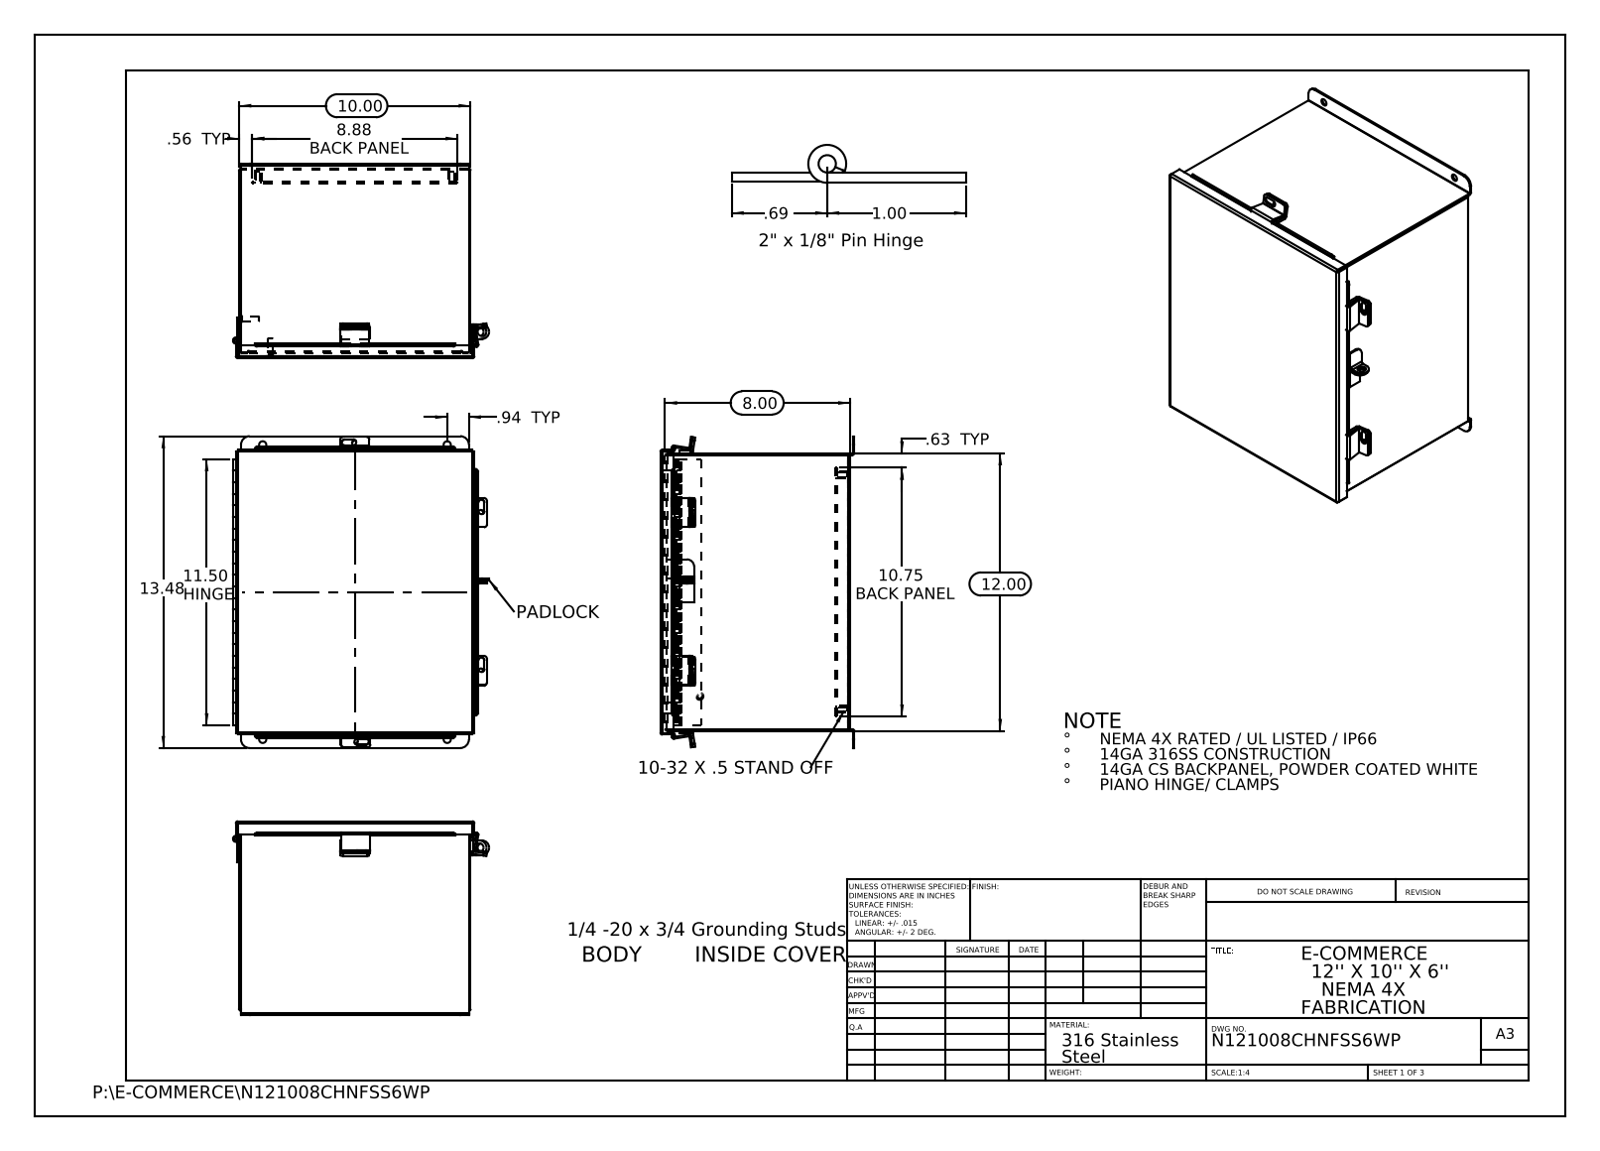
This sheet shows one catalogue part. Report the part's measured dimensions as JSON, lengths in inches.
{"part_name": "N121008CHNFSS6WP JIC Enclosure Template; N121008CHNFSS6WP JIC Top; N121008CHNFSS6WP JIC Cover Clamp; N121008CHNFSS6WP HW-CD-S-25020-034 (+8 more)", "step_written_by": "SolidWorks 2013 (CONFIG_CONTROL_DESIGN)", "units": "inches", "bodies": {"solids": 23, "faces": 702, "planar": 435, "cylindrical": 247, "other": 20}, "overall_size": [13.476, 11.072, 8.39], "volume_in3": 58.29, "surface_area_in2": 1590, "round_holes": [[0.25, 8], [0.187, 4], [0.312, 4], [0.125, 1], [0.125, 1], [0.373, 1], [0.375, 1]], "round_bosses_or_shafts": [[0.313, 4], [0.315, 2], [0.236, 2], [0.273, 1], [0.25, 1]], "partial_cylinders_radius": [[0.125, 15], [0.013, 13], [0.009, 12], [0.088, 12], [0.133, 8], [0.083, 6], [0.1, 6], [0.375, 4]], "face_to_face_distances": [0.075, 8.128, 9.925, 11.925, 8.053, 8.203, 0.074, 0.575, 0.5, 7.553], "hole_center_spacings": [1.315, 8.278, 11.428, 14.05, 7.976, 8.375, 10.126, 12.726]}
